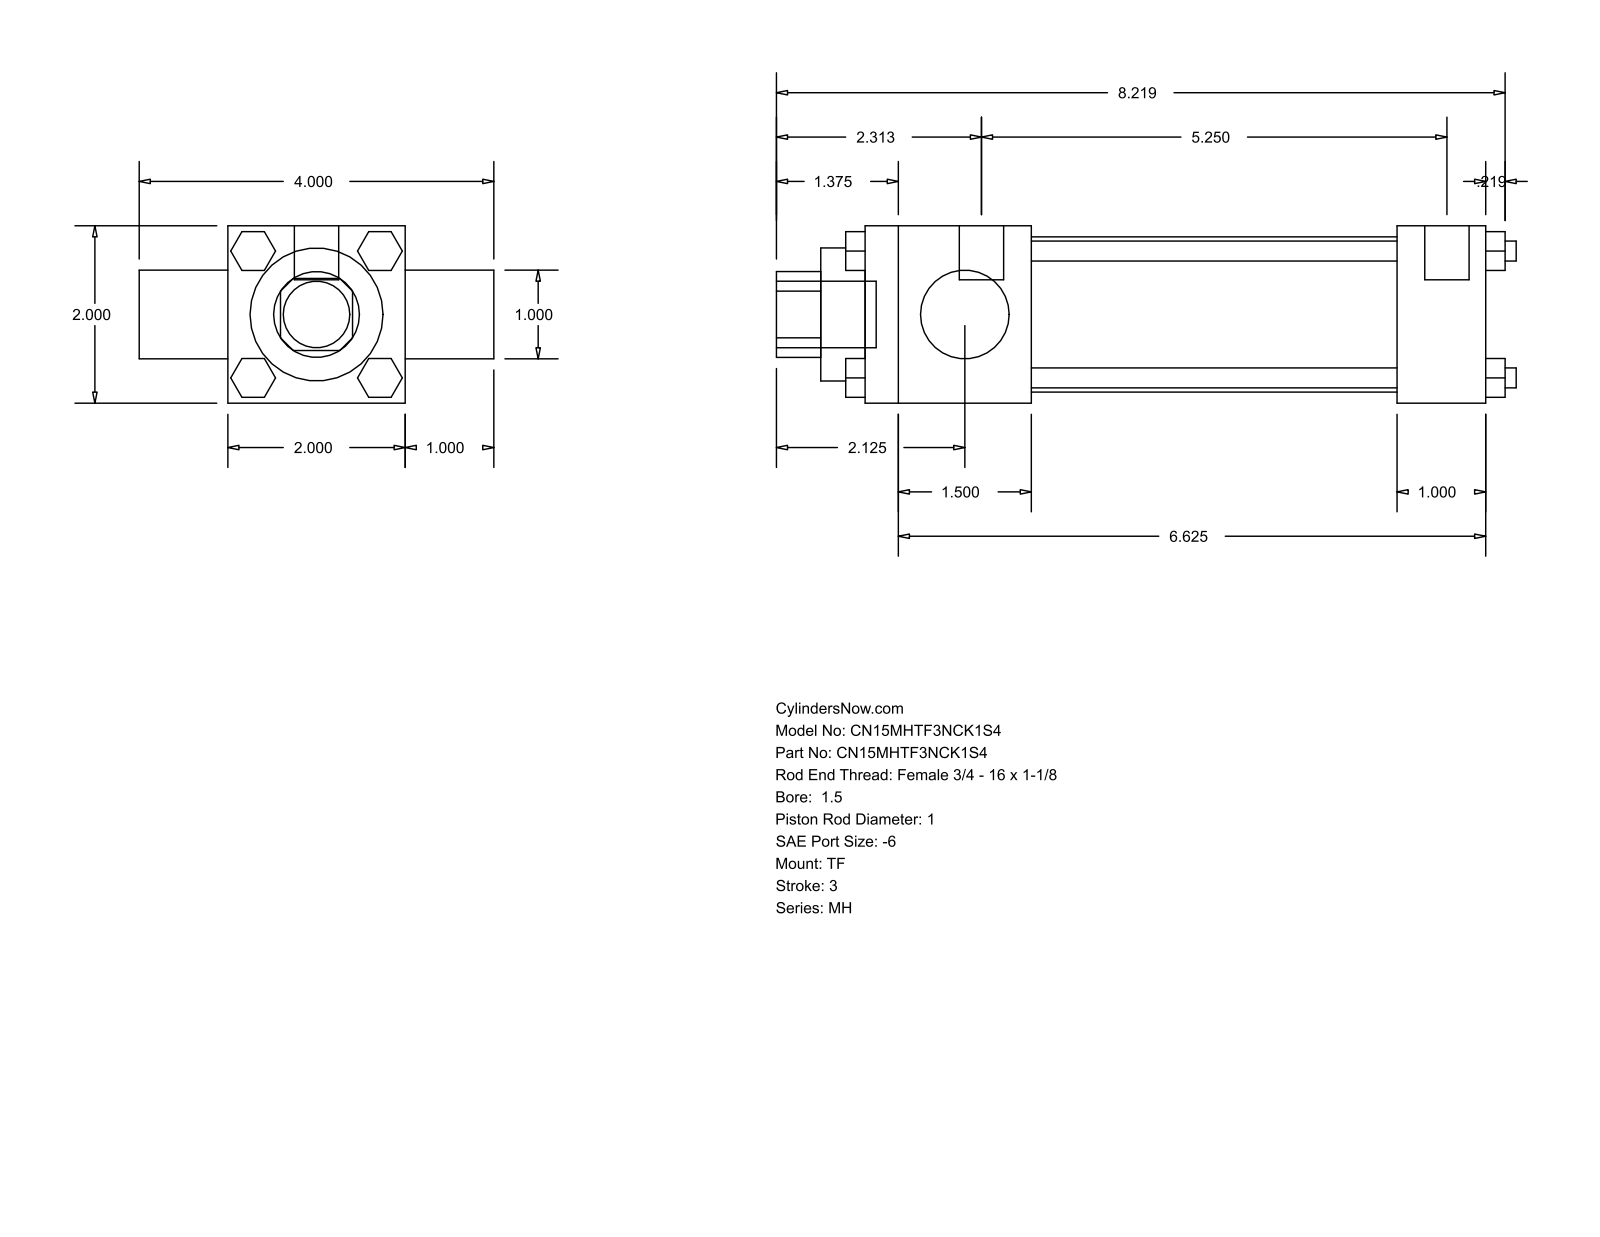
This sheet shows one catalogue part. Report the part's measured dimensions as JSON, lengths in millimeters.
{"part_name": "MH_TF__0150_1", "step_written_by": "GSSL Pune (CONFIG_CONTROL_DESIGN)", "units": "millimeters", "bodies": {"solids": 0, "faces": 120, "planar": 92, "cylindrical": 28, "other": 0}, "overall_size": [211.93, 101.6, 50.8], "round_holes": [[25.4, 2], [38.1, 1], [44.45, 1]], "round_bosses_or_shafts": [[5.71, 4], [5.56, 3], [12.7, 2], [19.05, 1]], "partial_cylinders_radius": [[12.29, 1]], "face_to_face_distances": [50.8, 25.4, 177.8, 76.2, 47.63, 130.17, 152.4, 104.77, 183.36, 12.7]}
